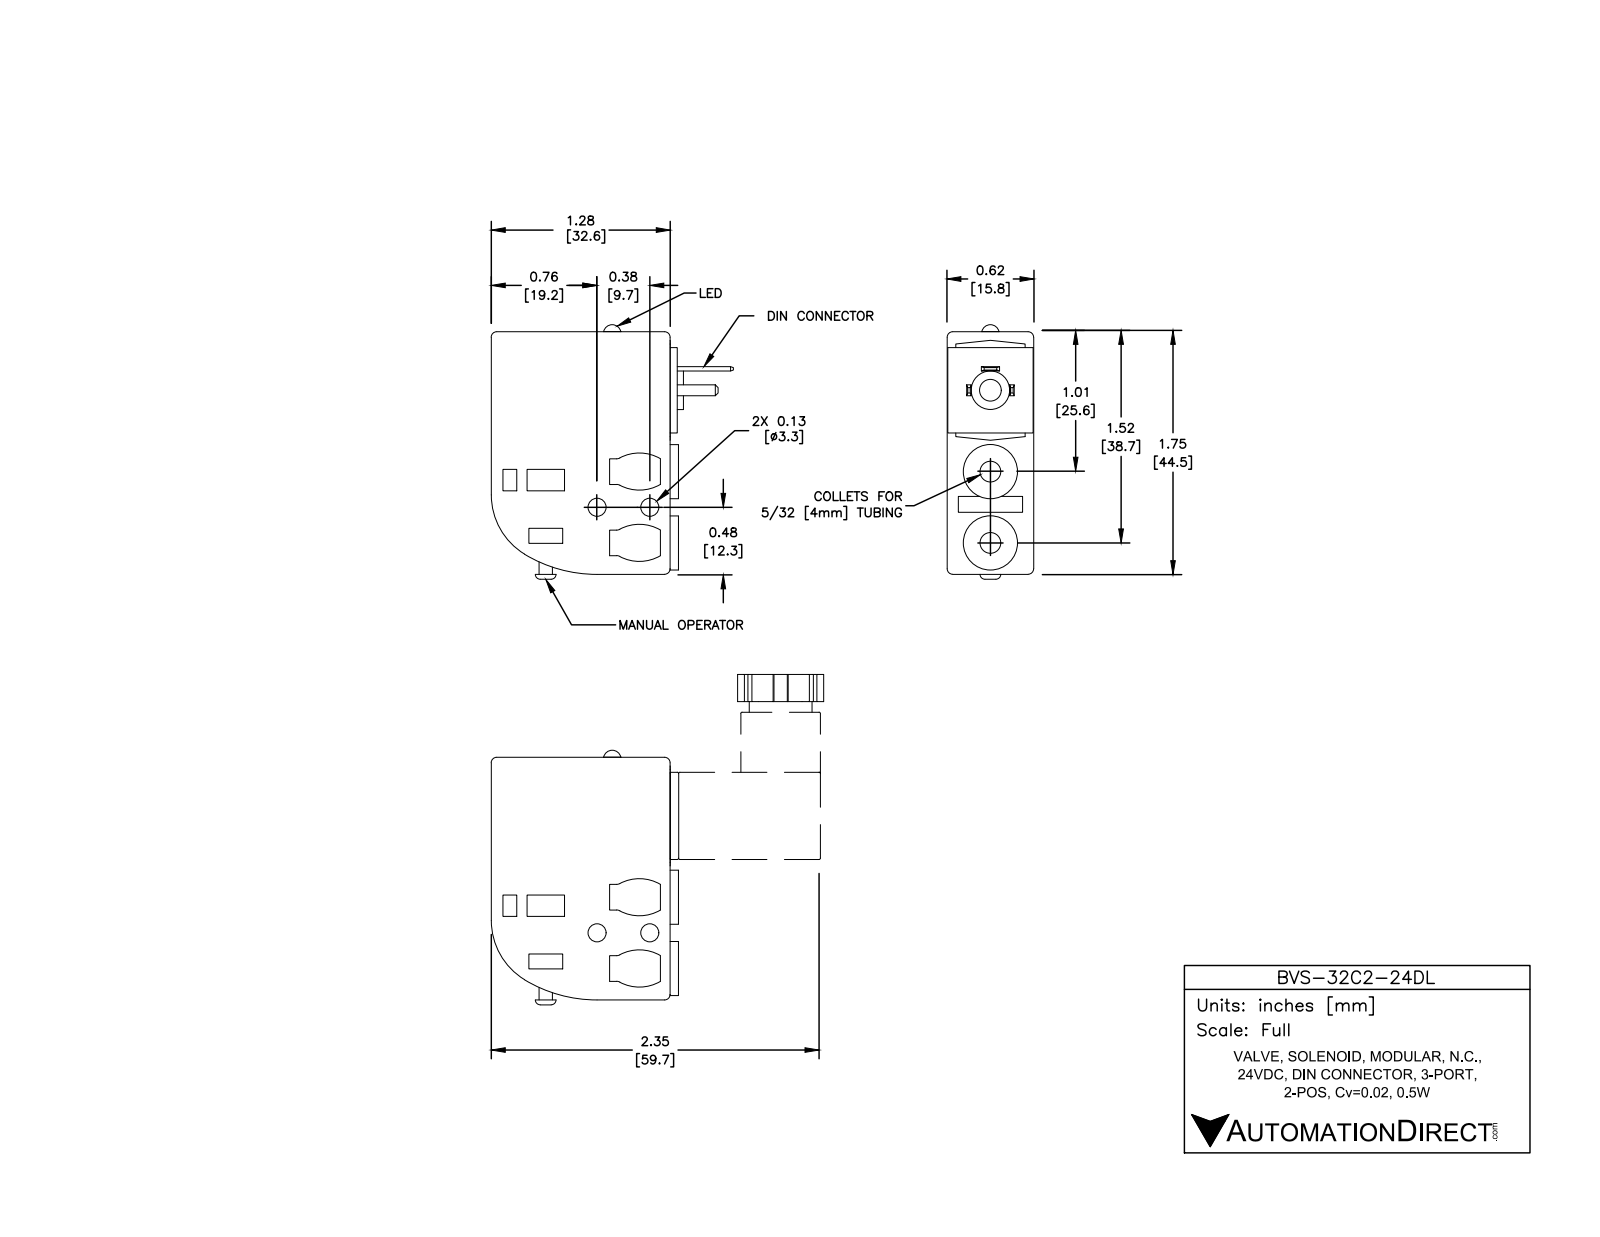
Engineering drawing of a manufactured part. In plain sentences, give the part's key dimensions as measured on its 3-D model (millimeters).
The part is named "BVS-32C2-24DL". Its 3-D file was written by "SolidWorks 2016 (AUTOMOTIVE_DESIGN)". It is 1 solid with 162 faces: 112 planar, 46 cylindrical and 4 other. Overall it measures 46.7 by 44.5 by 15.7 millimeters. Its volume is 20 960 cubic millimeters and its surface area 6 935 square millimeters. Round holes: 2 of diameter 3.3, 2 of diameter 3.8, 2 of diameter 6.4, 1 of diameter 1.3, 1 of diameter 4.1. Round bosses or shafts: 2 of diameter 9.9, 1 of diameter 7.1, 1 of diameter 2.5. Partial cylindrical surfaces (rounded edges, fillets, slot ends): 4 of radius 1.3, 4 of radius 7.6, 3 of radius 1, 1 of radius 12.7, 1 of radius 25.4. The main face-to-face distances are 15.7, 2.5, 32.8, 13.2, 34.1, 1.3, 44.5, 25.4, 3.8, 1.5. The hole center spacings are 1.5, 9.7, 11.4, 13, 15, 16.5, 27.9.
